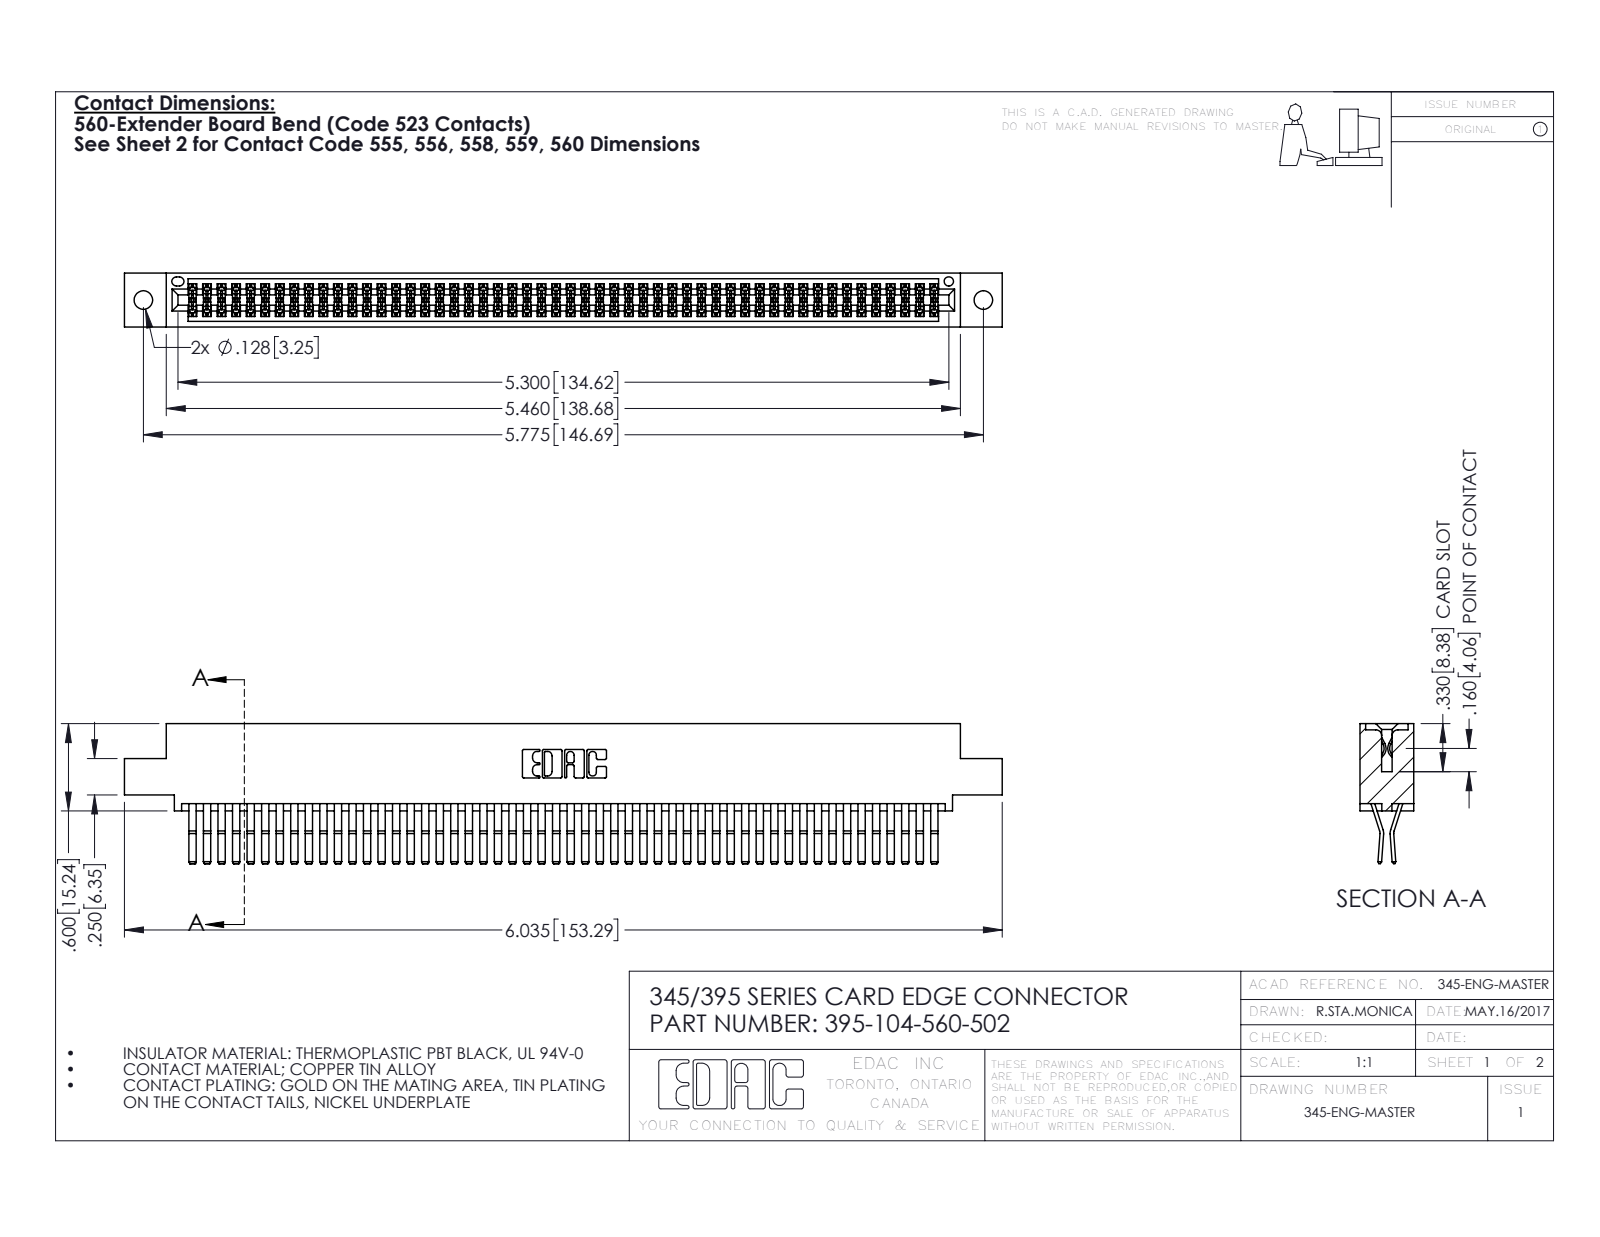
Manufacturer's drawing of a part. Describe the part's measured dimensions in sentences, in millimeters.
The part is named "395-104-560-502; 345-292-001_560 Tail; 345 Part_0.110 Offset - 0.128 Dia". Its 3-D file was written by "SolidWorks 2016 (CONFIG_CONTROL_DESIGN)". It is 105 solids with 5538 faces: 3516 planar, 2022 cylindrical and 0 other. Overall it measures 153.3 by 24.4 by 9.4 millimeters. Its volume is 15 600 cubic millimeters and its surface area 24 760 square millimeters. Round holes: 2 of diameter 3.3, 1 of diameter 1.6. Partial cylindrical surfaces (rounded edges, fillets, slot ends): 157 of radius 0.2, 22 of radius 0.3, 6 of radius 0.2, 6 of radius 0.8, 3 of radius 0.7, 2 of radius 0.3, 2 of radius 0.4, 2 of radius 0.5. The main face-to-face distances are 0.6, 7.6, 1.8, 9.4, 5.1, 2.5, 6.9, 5.7, 4.4, 3.8. The hole center spacings are 6.9, 140.7, 146.7.
